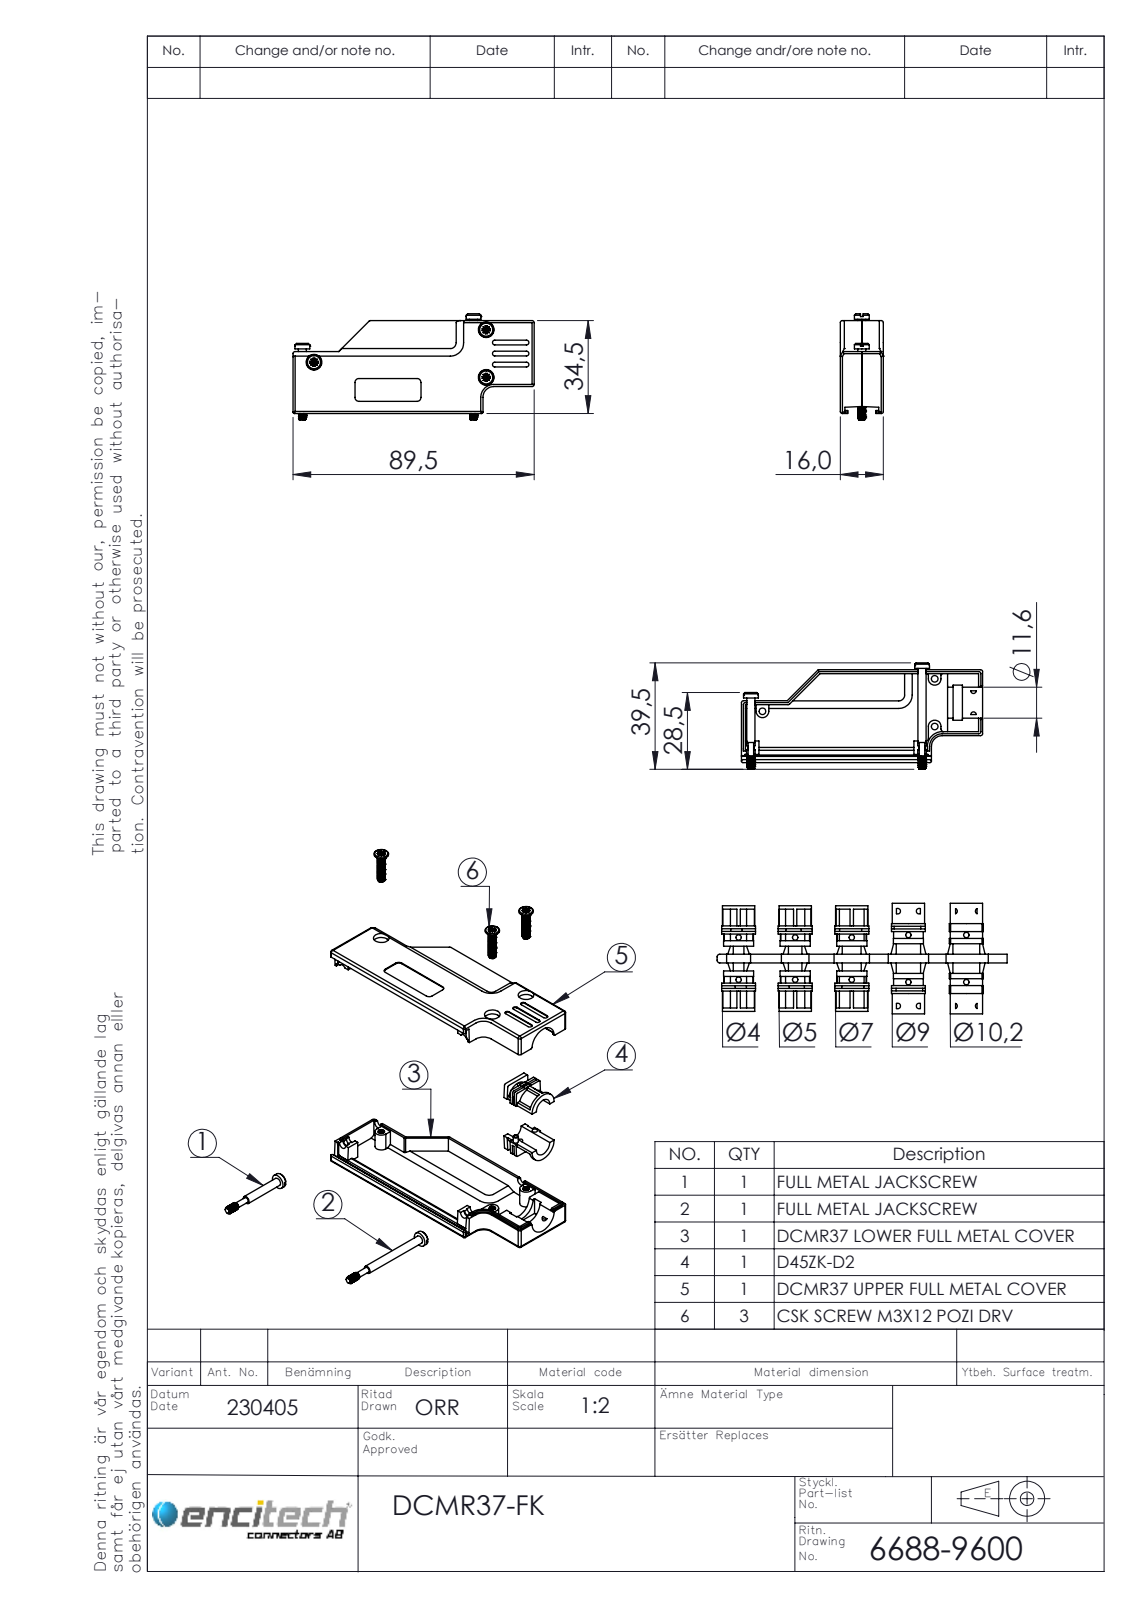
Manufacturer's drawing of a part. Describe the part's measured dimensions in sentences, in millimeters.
The part is named "6855-0117-02; 6688-9600; 6805-0501-14; 6826-0128-12 (+3 more)". Its 3-D file was written by "SolidWorks 2021 (AUTOMOTIVE_DESIGN)". It is 9 solids with 928 faces: 388 planar, 444 cylindrical and 96 other. Overall it measures 89.5 by 39.5 by 16 millimeters. Its volume is 14 601 cubic millimeters and its surface area 19 631 square millimeters. Round holes: 3 of diameter 2, 3 of diameter 5.8, 2 of diameter 2.46, 2 of diameter 3.2, 1 of diameter 2.45, 1 of diameter 7, 1 of diameter 11.6. Round bosses or shafts: 3 of diameter 2.9, 2 of diameter 5.5, 2 of diameter 3, 2 of diameter 2.84, 2 of diameter 2, 2 of diameter 1.9, 1 of diameter 9.2. Partial cylindrical surfaces (rounded edges, fillets, slot ends): 23 of radius 0.8, 18 of radius 0.5, 12 of radius 0.1, 6 of radius 0.9, 6 of radius 1, 4 of radius 1.5, 4 of radius 2.25, 4 of radius 5.91. The main face-to-face distances are 1.3, 1.5, 14.7, 13.2, 16, 13.4, 8, 13, 5.2, 6.7. The hole center spacings are 5.71, 9.29, 10.53, 16.22, 10, 17.7, 63.5, 64.15.
